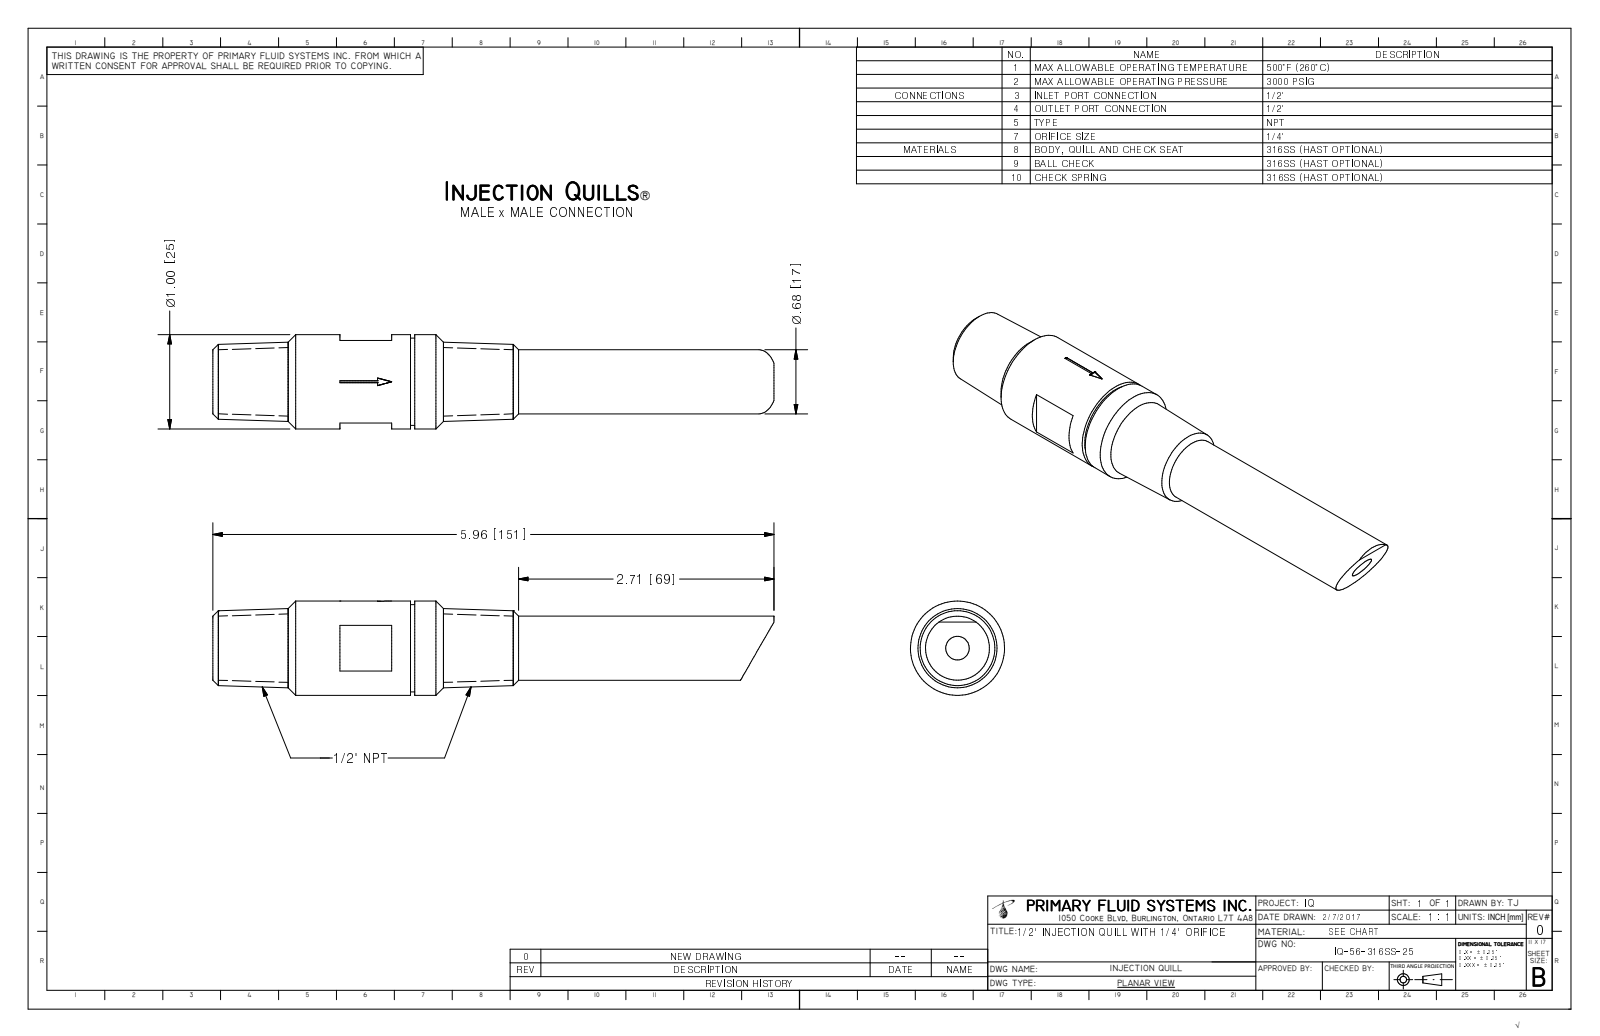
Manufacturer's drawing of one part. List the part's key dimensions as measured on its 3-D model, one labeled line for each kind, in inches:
Part name (STEP PRODUCT): IQ-56-316SS-25_R0
STEP written by: Autodesk Inventor 2009 (AUTOMOTIVE_DESIGN)
Units: inches
Bodies: 1 solid, 33 faces (18 planar, 7 cylindrical, 8 other)
Overall size (bounding box): 5.964 × 1 × 1
Volume: 2.698 in³ · Surface area: 19.91 in²
Round holes (diameter × count): ⌀0.25 ×1, ⌀0.469 ×1
Round bosses / shafts (diameter × count): ⌀1 ×1, ⌀0.925 ×1, ⌀0.679 ×1
Partial cylindrical surfaces — rounded edges, fillets, slot ends (radius × count): R0.499 ×1
Main face-to-face distances: 0.875, 0.75, 1.35, 2.1, 2.145, 1.395, 0.045, 0.15, 2.25, 1.5
